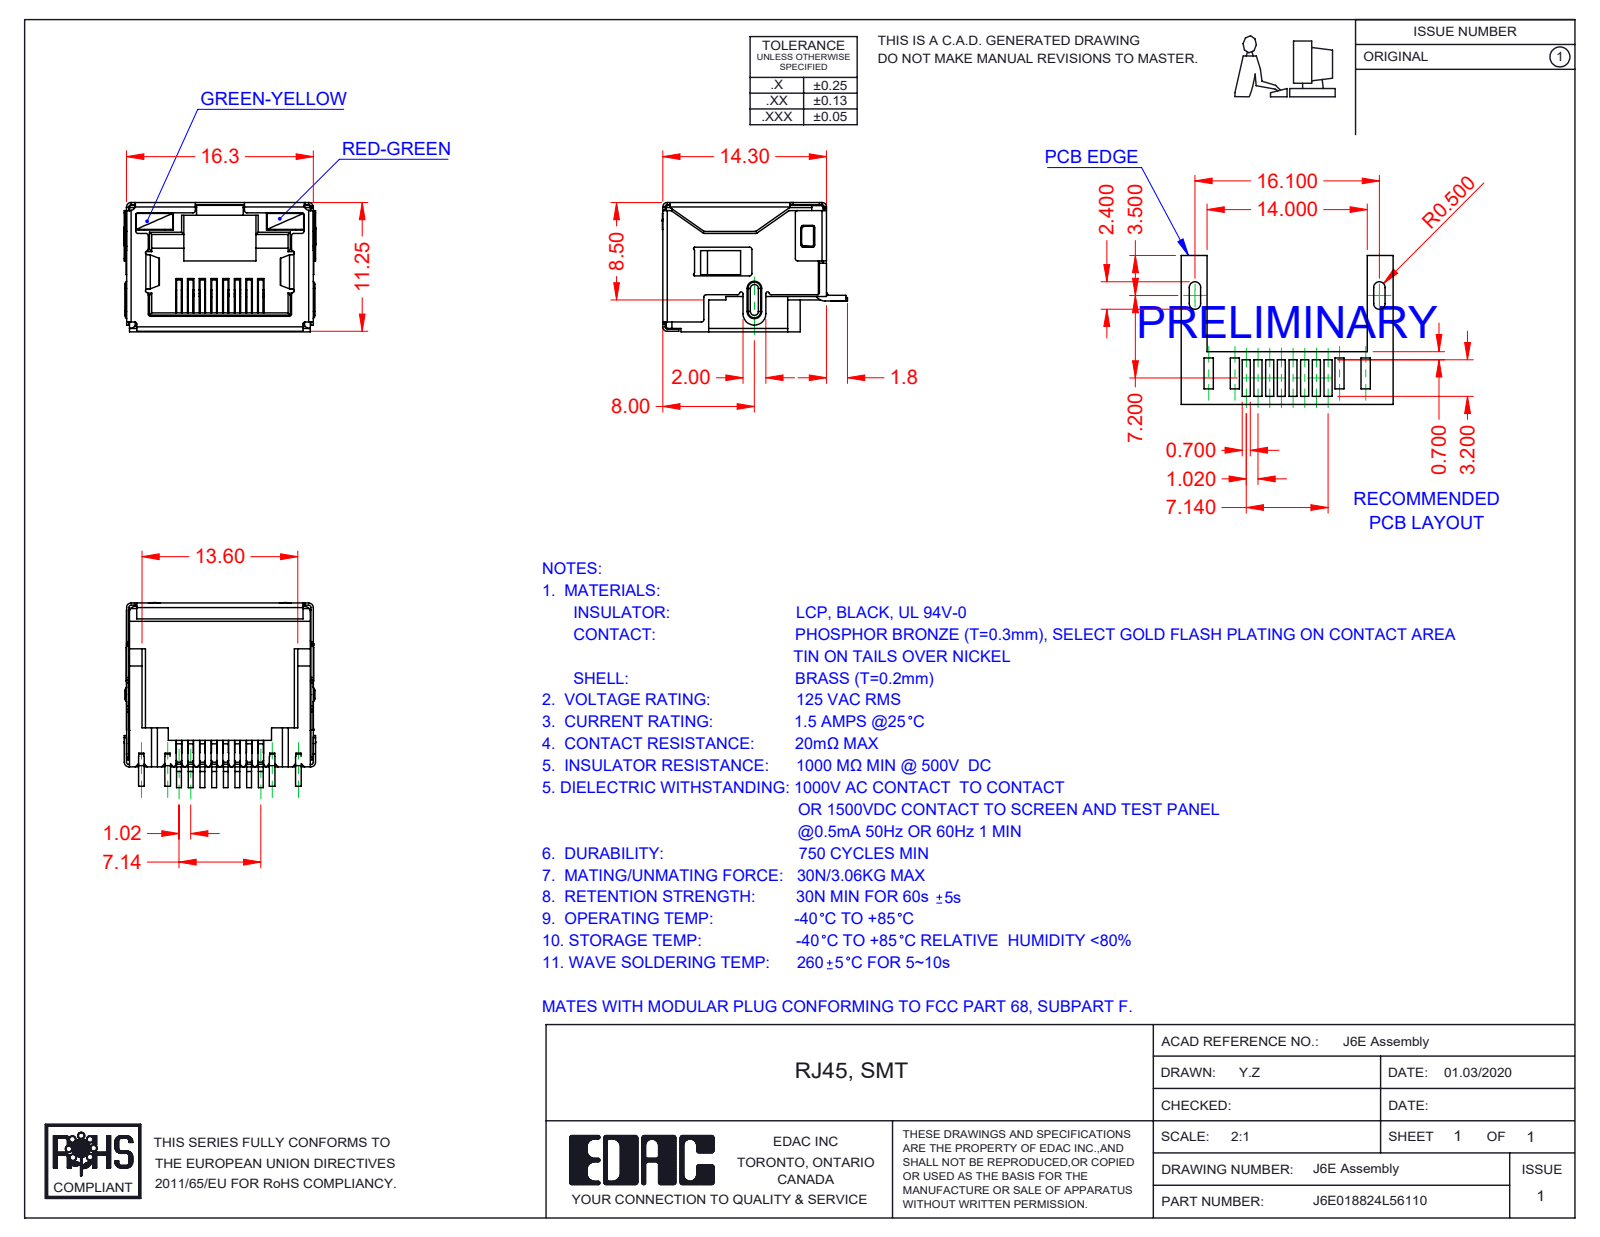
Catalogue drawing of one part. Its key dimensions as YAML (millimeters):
part_name: "6E LED RH_6-Red-Green; 6E Shield_LED; 6E LED LH_5-Green-Yellow; 6E Contacts (+2 more)"
step_written_by: "SolidWorks 2016 (CONFIG_CONTROL_DESIGN)"
units: millimeters
bodies: {solids: 12, faces: 1500, planar: 1099, cylindrical: 351, other: 50}
overall_size: [16.75, 16.15, 11.3]
volume: 1109
surface_area: 4045
partial_cylinders:
  - {radius: 0.2, count: 82}
  - {radius: 0.25, count: 17}
  - {radius: 0.4, count: 13}
  - {radius: 0.5, count: 13}
  - {radius: 0.1, count: 10}
  - {radius: 0.15, count: 7}
  - {radius: 0.3, count: 4}
  - {radius: 1, count: 3}
face_to_face_distances: [11.05, 16.05, 16.1, 15.85, 11.1, 11.3, 2.4, 0.7, 9.85, 0.49]
